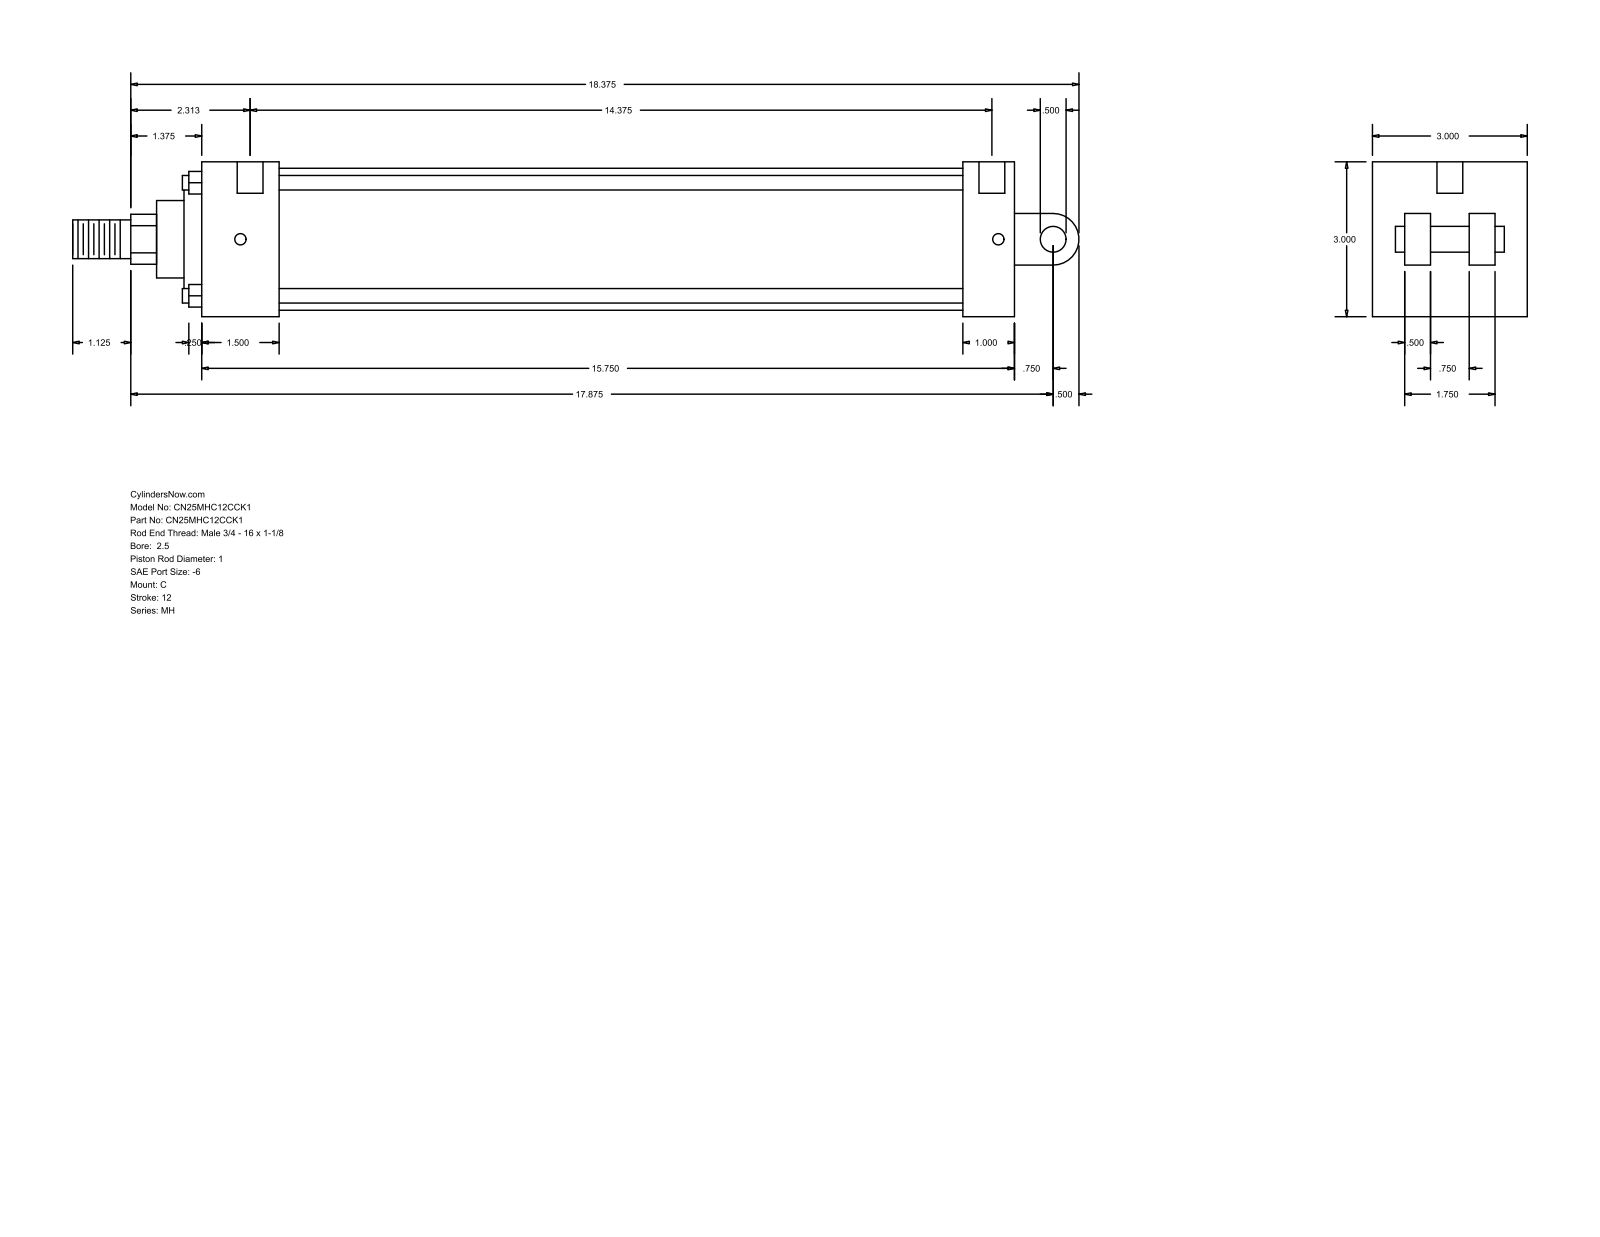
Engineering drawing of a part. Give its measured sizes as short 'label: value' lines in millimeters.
name: MH_C__0250_1
written by: GSSL Pune (CONFIG_CONTROL_DESIGN)
unit: mm
bodies: 0 solids, 101 faces (71 planar, 30 cylindrical, 0 other)
size: 495.3 × 76.2 × 76.2
holes: 4× ⌀5.56, 2× ⌀12.7
bosses: 4× ⌀7.14, 1× ⌀69.85, 1× ⌀60.33, 1× ⌀38.1, 1× ⌀25.4, 1× ⌀19.05, 1× ⌀12.7
rounds: 1× R12.29, 1× R12.7
face distances: 76.2, 400.06, 60.33, 15.87, 374.65, 25.41, 38.11, 336.54, 361.95, 12.7
hole spacings: 373.06, 3.18, 4.76, 365.12, 368.3, 369.88
